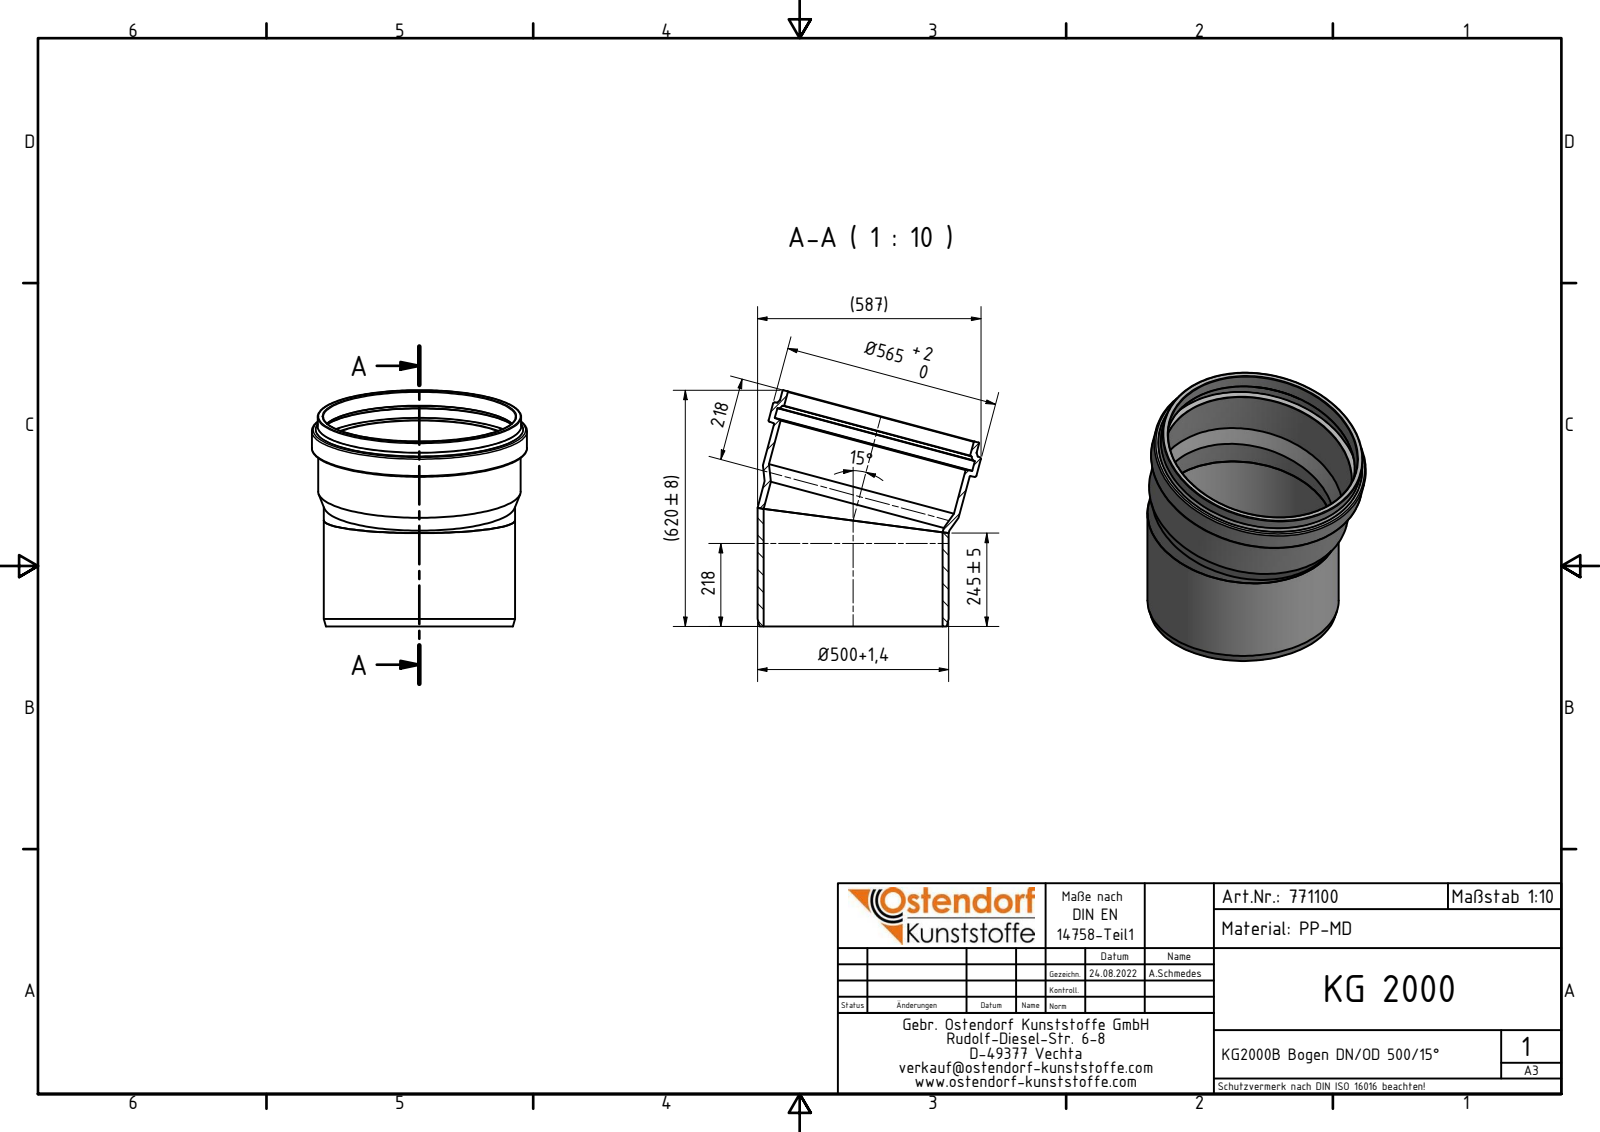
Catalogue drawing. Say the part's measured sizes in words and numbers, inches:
The part is named "771100 KG2000B Bogen DN_OD 500x15°; 771100 KG2000B Bogen DN_OD 500x15° Teil 1; 771100 KG2000B Bogen DN_OD 500x15° Teil 2". Its 3-D file was written by "Autodesk Inventor 2020 (AUTOMOTIVE_DESIGN)". It is 2 solids with 37 faces: 4 planar, 10 cylindrical and 23 other. Overall it measures 24.22 by 23.296 by 22.244 inches. Its volume is 866.5 cubic inches and its surface area 3 009 square inches. Round holes: 2 of diameter 18.504, 1 of diameter 19.802, 1 of diameter 19.895, 1 of diameter 21.129. Round bosses or shafts: 2 of diameter 19.764, 1 of diameter 22.244, 1 of diameter 21.032, 1 of diameter 20.939.
